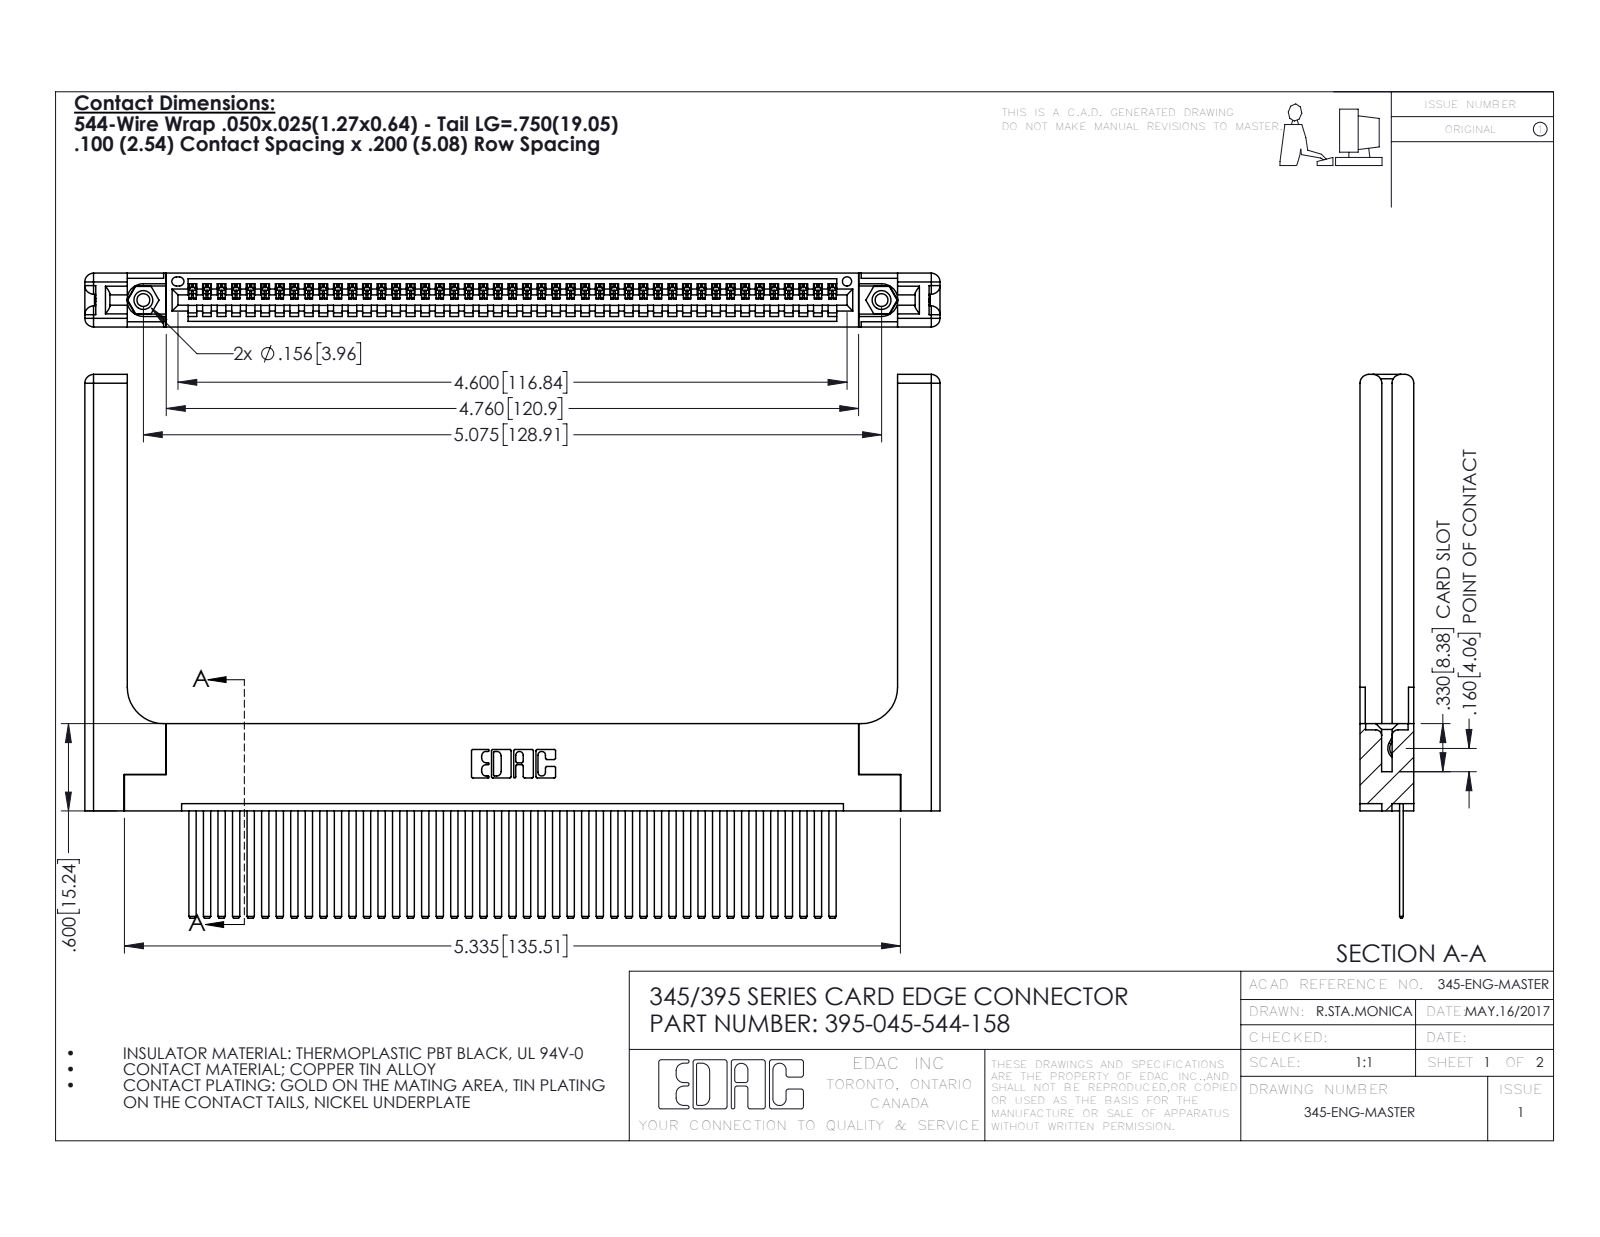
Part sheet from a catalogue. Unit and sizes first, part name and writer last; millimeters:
Units: millimetres
Overall size (bounding box): 149.3 × 94.9 × 9.4
Round holes (diameter × count): ⌀2.3 ×2, ⌀3.2 ×2, ⌀4 ×2, ⌀1.6 ×1
Round bosses / shafts (diameter × count): ⌀3.9 ×2
Partial cylindrical surfaces — rounded edges, fillets, slot ends (radius × count): R0.2 ×90, R0.3 ×22, R1.5 ×16, R0.2 ×6, R0.8 ×6, R0.7 ×3, R0.8 ×2, R0.8 ×2
Main face-to-face distances: 1.8, 7.6, 9.4, 2.5, 6.9, 0.6, 5.1, 5.7, 3.8, 3.8
Hole centre spacings: 6.9, 122.9, 128.9
Volume: 23 240 mm³ · Surface area: 26 480 mm²
Bodies: 50 solids, 2722 faces (1848 planar, 814 cylindrical, 60 other)
Part name (STEP PRODUCT): 345-250-001_345-250-001-102; 345 Part_Flush Mounting Lugs - 0.156 Dia-TH; 345-292-001_345-293-144; 395-045-544-158 (+1 more)
STEP written by: SolidWorks 2016 (CONFIG_CONTROL_DESIGN)
